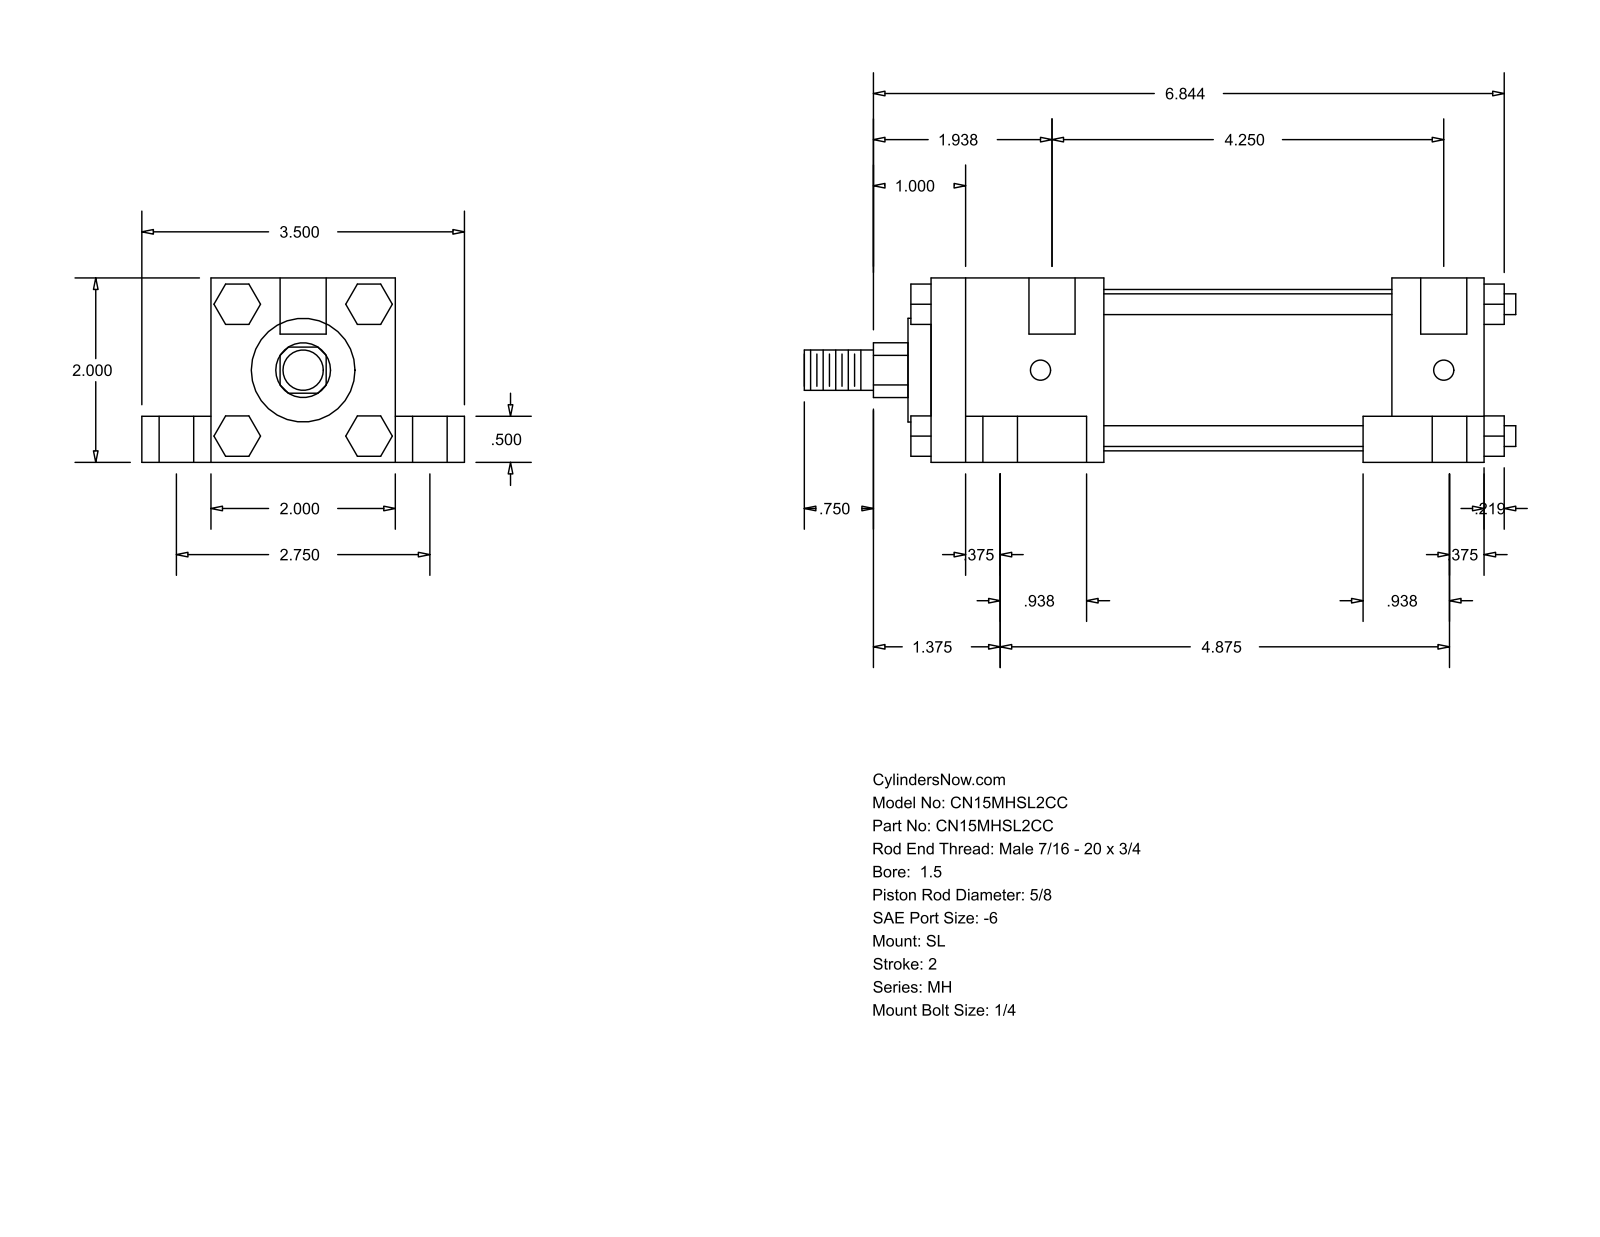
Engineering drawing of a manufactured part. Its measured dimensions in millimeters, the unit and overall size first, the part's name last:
Units: millimetres
Overall size (bounding box): 196.06 × 88.9 × 50.8
Round holes (diameter × count): ⌀5.56 ×4, ⌀9.53 ×4, ⌀15.88 ×4, ⌀12.7 ×2
Round bosses / shafts (diameter × count): ⌀5.71 ×4, ⌀44.45 ×1, ⌀28.57 ×1, ⌀15.88 ×1, ⌀11.11 ×1
Partial cylindrical surfaces — rounded edges, fillets, slot ends (radius × count): R7.54 ×1
Main face-to-face distances: 50.8, 38.1, 19.05, 12.7, 69.85, 152.4, 25.4, 9.52, 33.34, 109.54
Hole centre spacings: 34.96, 36.65, 37.73, 69.84, 111.12, 114.97, 118, 123.83
Bodies: 0 solids, 148 faces (112 planar, 36 cylindrical, 0 other)
Part name (STEP PRODUCT): MH_SL__0150_0.625
STEP written by: GSSL Pune (CONFIG_CONTROL_DESIGN)
